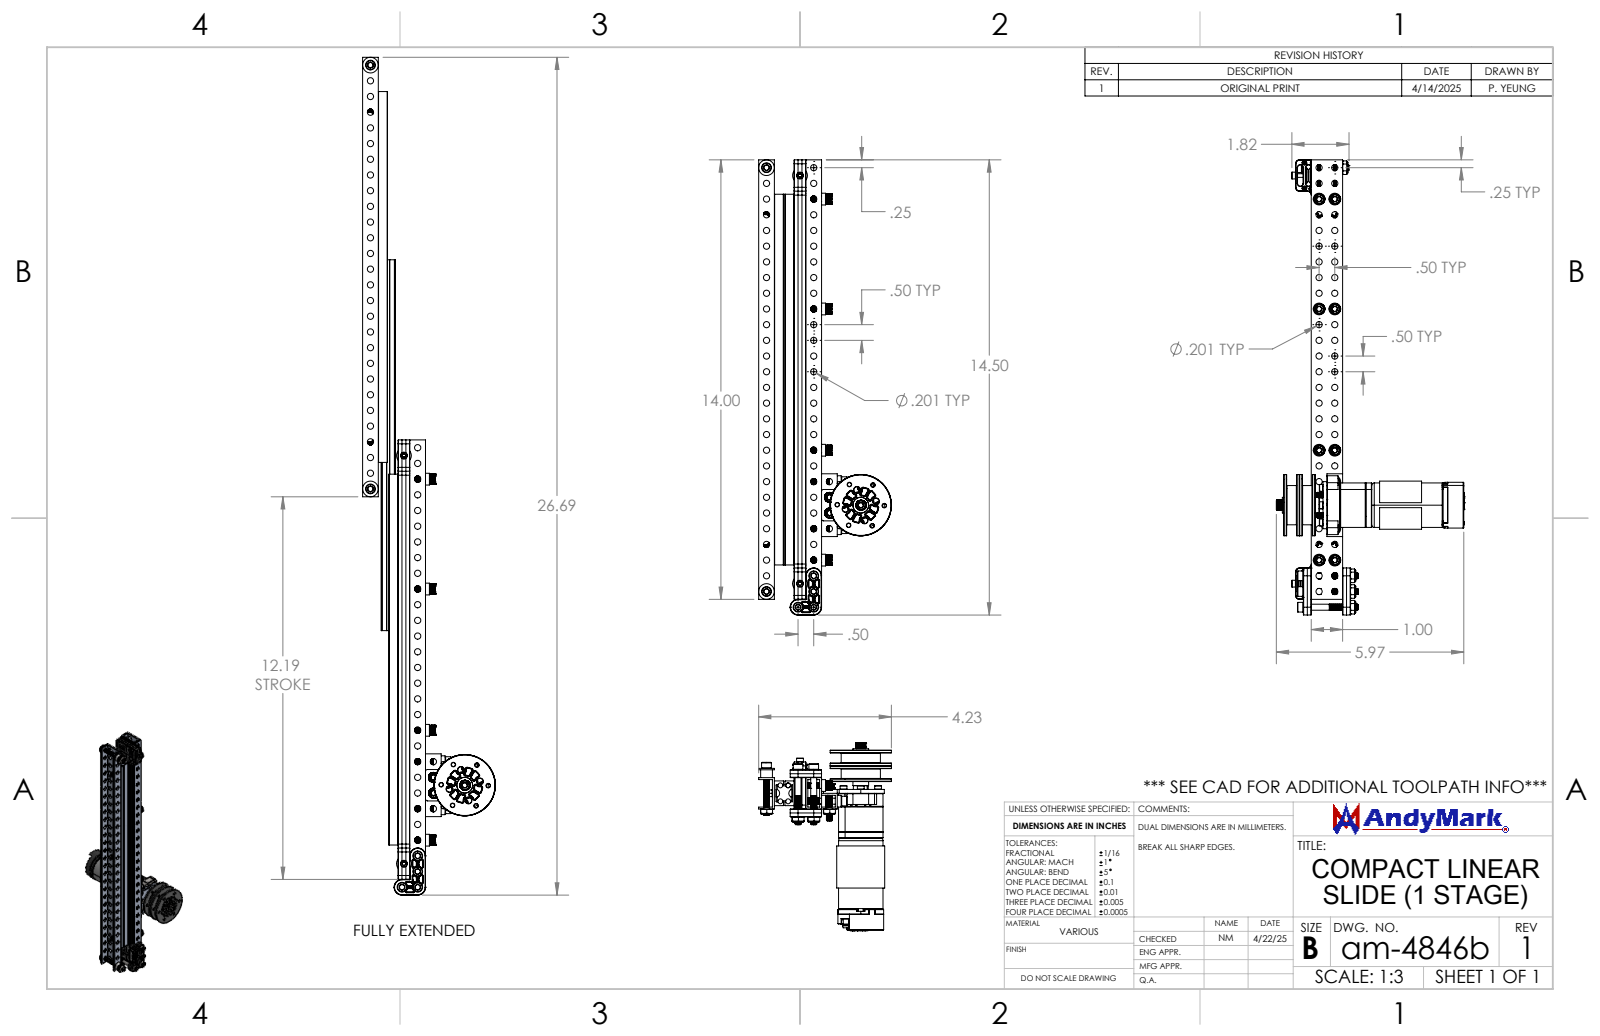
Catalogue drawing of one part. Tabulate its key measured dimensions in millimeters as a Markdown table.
| quantity | value |
| --- | --- |
| part name | am-3104c NeveRest Hex Motor; am-1742 0.430 ID 0.500 OD 0.125 Long Aluminum Spacer; 12x21x9 Bearing; NeveRest Hex Shaft 375H 1IN Long (+8 more) |
| STEP written by | SolidWorks 2024 (AUTOMOTIVE_DESIGN) |
| units | millimeters |
| bodies | 161 solids, 28773 faces (5267 planar, 9165 cylindrical, 14341 other) |
| overall size | 368.3 × 152 × 107.5 |
| volume | 326 600 mm³ |
| surface area | 310 100 mm² |
| round holes (diameter × count) | 5.1 × 122, 4.2 × 72, 4.1 × 18, 6.1 × 18, 3.2 × 13, 4.9 × 11, 2.5 × 10, 0.6 × 9, 3.2 × 9, 3.2 × 6, 4 × 5, 0.9 × 4 |
| round bosses / shafts (diameter × count) | 4.8 × 19, 9.5 × 13, 3 × 13, 8 × 11, 5.5 × 10, 7.9 × 8, 2.4 × 8, 0.7 × 6 |
| partial cylindrical surfaces (radius × count) | 0.3 × 1452, 0.2 × 97, 0.1 × 92, 0.1 × 75, 0.3 × 74, 0.5 × 59, 0.8 × 32, 0.5 × 24 |
| main face-to-face distances | 12.7, 1.6, 11.1, 9.5, 22.2, 1.6, 25.4, 25.5, 38.2, 11.1 |
| hole center spacings | 12.7, 25.4, 38.1, 50.8, 63.5, 76.2, 88.9, 101.6 |
